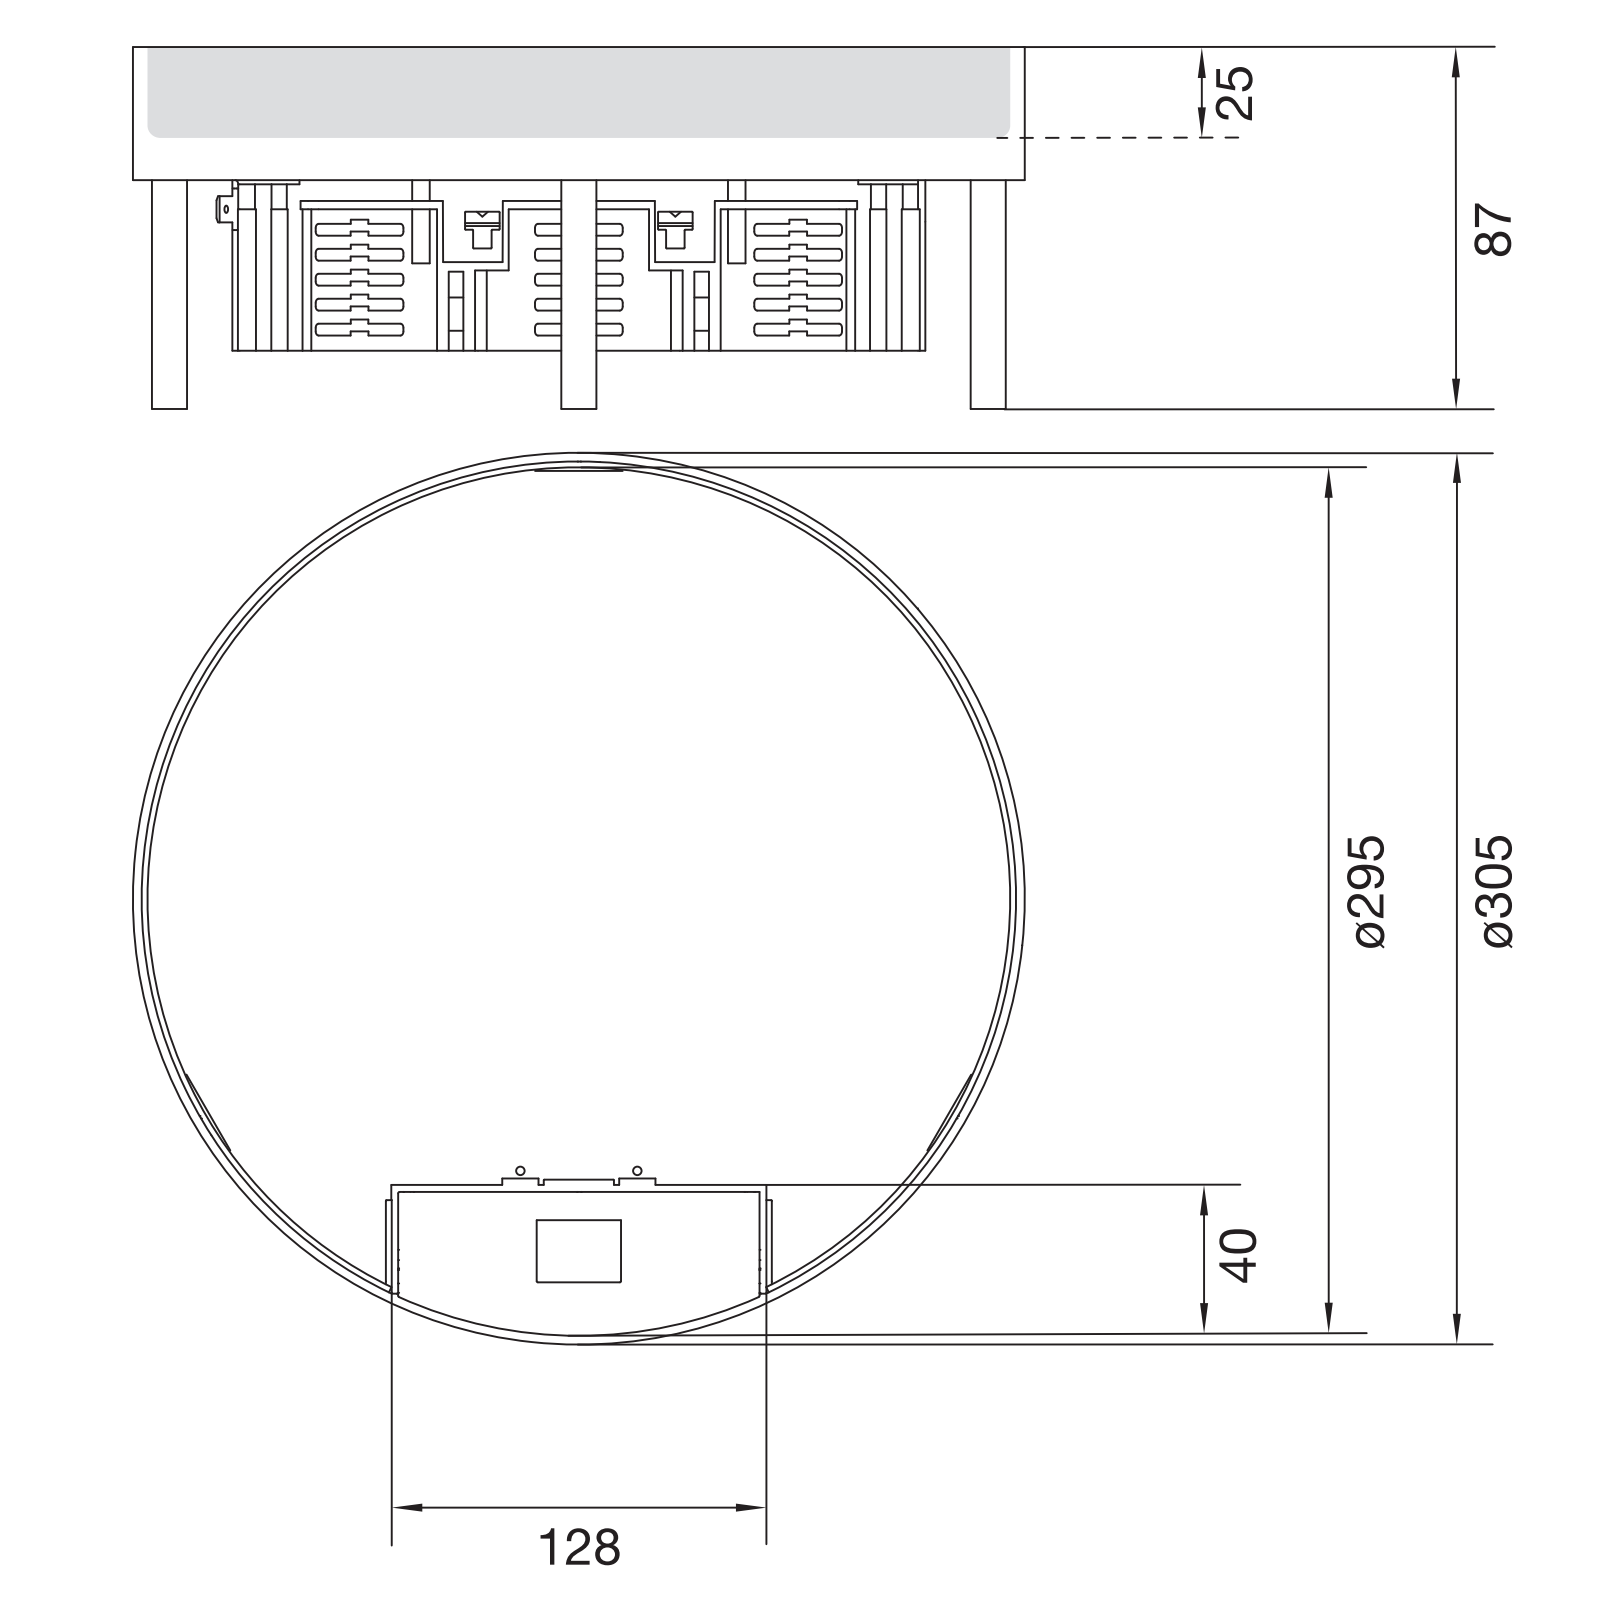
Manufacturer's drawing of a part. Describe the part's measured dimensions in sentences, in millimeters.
The part is named "T-00736; T-00737; T-00738; T-00739 (+8 more)". Its 3-D file was written by "CREO PARAMETRIC BY PTC INC, 2022024 (AUTOMOTIVE_DESIGN)". It is 15 solids with 271 faces: 170 planar, 85 cylindrical and 16 other. Overall it measures 305 by 305 by 87 millimeters. Its volume is 402 310 cubic millimeters and its surface area 400 567 square millimeters. Round holes: 6 of diameter 3.8, 4 of diameter 6.8, 4 of diameter 8.5, 4 of diameter 10.1, 2 of diameter 2.5. Round bosses or shafts: 4 of diameter 12, 4 of diameter 9.85, 1 of diameter 305, 1 of diameter 301, 1 of diameter 299, 1 of diameter 295. Partial cylindrical surfaces (rounded edges, fillets, slot ends): 10 of radius 0.5, 3 of radius 0.3, 1 of radius 1.01, 1 of radius 6.6, 1 of radius 150. The main face-to-face distances are 2, 5, 2.5, 3, 7, 228.5, 229.5, 27, 25, 32. The hole center spacings are 59.51, 143.6, 197.99, 225.52, 260.65, 25.3, 40.44, 50.99.
